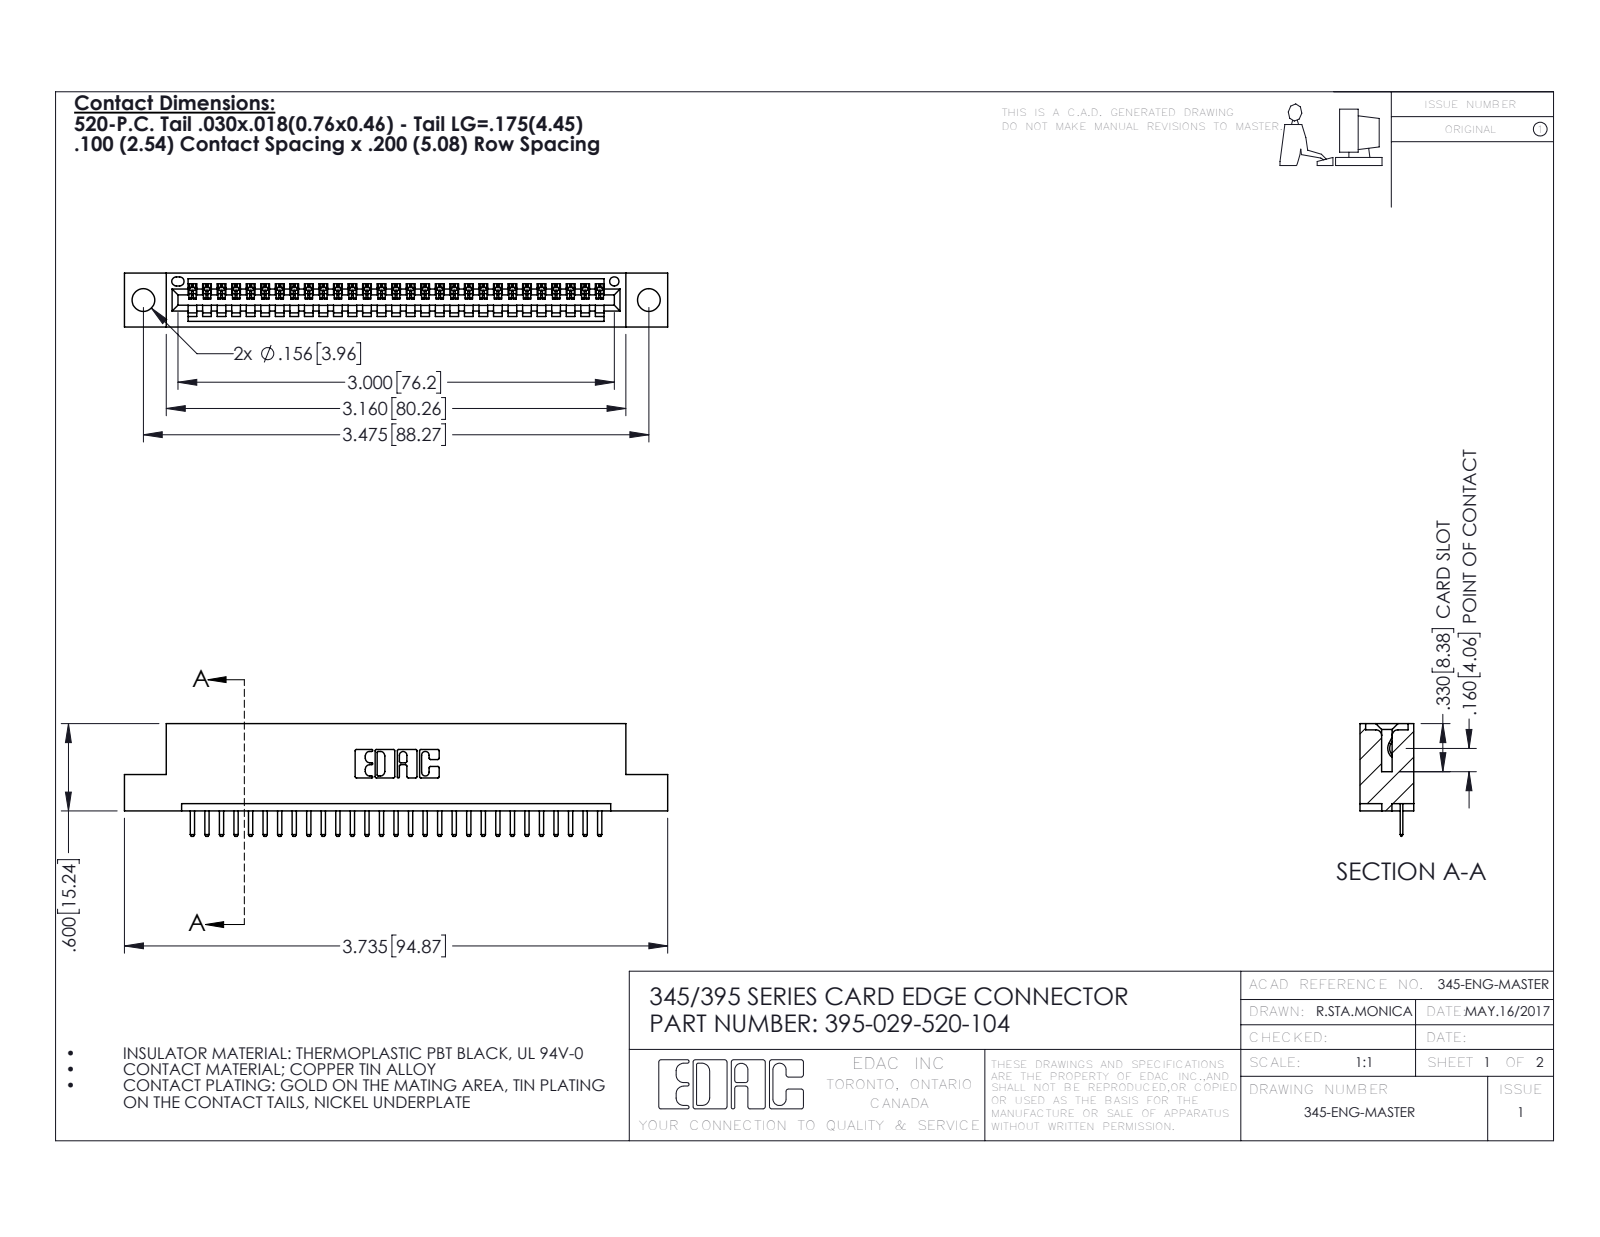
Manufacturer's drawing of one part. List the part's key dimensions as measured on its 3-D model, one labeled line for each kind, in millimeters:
Part name (STEP PRODUCT): 345 Part_Flush Mounting Lugs - 0.156 Dia-TH; 395-029-520-104; 345-292-001_345-293-120
STEP written by: SolidWorks 2016 (CONFIG_CONTROL_DESIGN)
Units: millimetres
Bodies: 30 solids, 1924 faces (1298 planar, 626 cylindrical, 0 other)
Overall size (bounding box): 94.9 × 19.7 × 9.4
Volume: 8 730 mm³ · Surface area: 10 970 mm²
Round holes (diameter × count): ⌀4 ×2, ⌀1.6 ×1
Partial cylindrical surfaces — rounded edges, fillets, slot ends (radius × count): R0.3 ×60, R0.2 ×58, R0.3 ×22, R0.2 ×6, R0.8 ×6, R0.7 ×3, R0.8 ×2, R1 ×2
Main face-to-face distances: 7.6, 1.8, 9.4, 5.1, 2.5, 6.9, 0.6, 5.7, 1.8, 3.8
Hole centre spacings: 6.9, 82.3, 88.3
